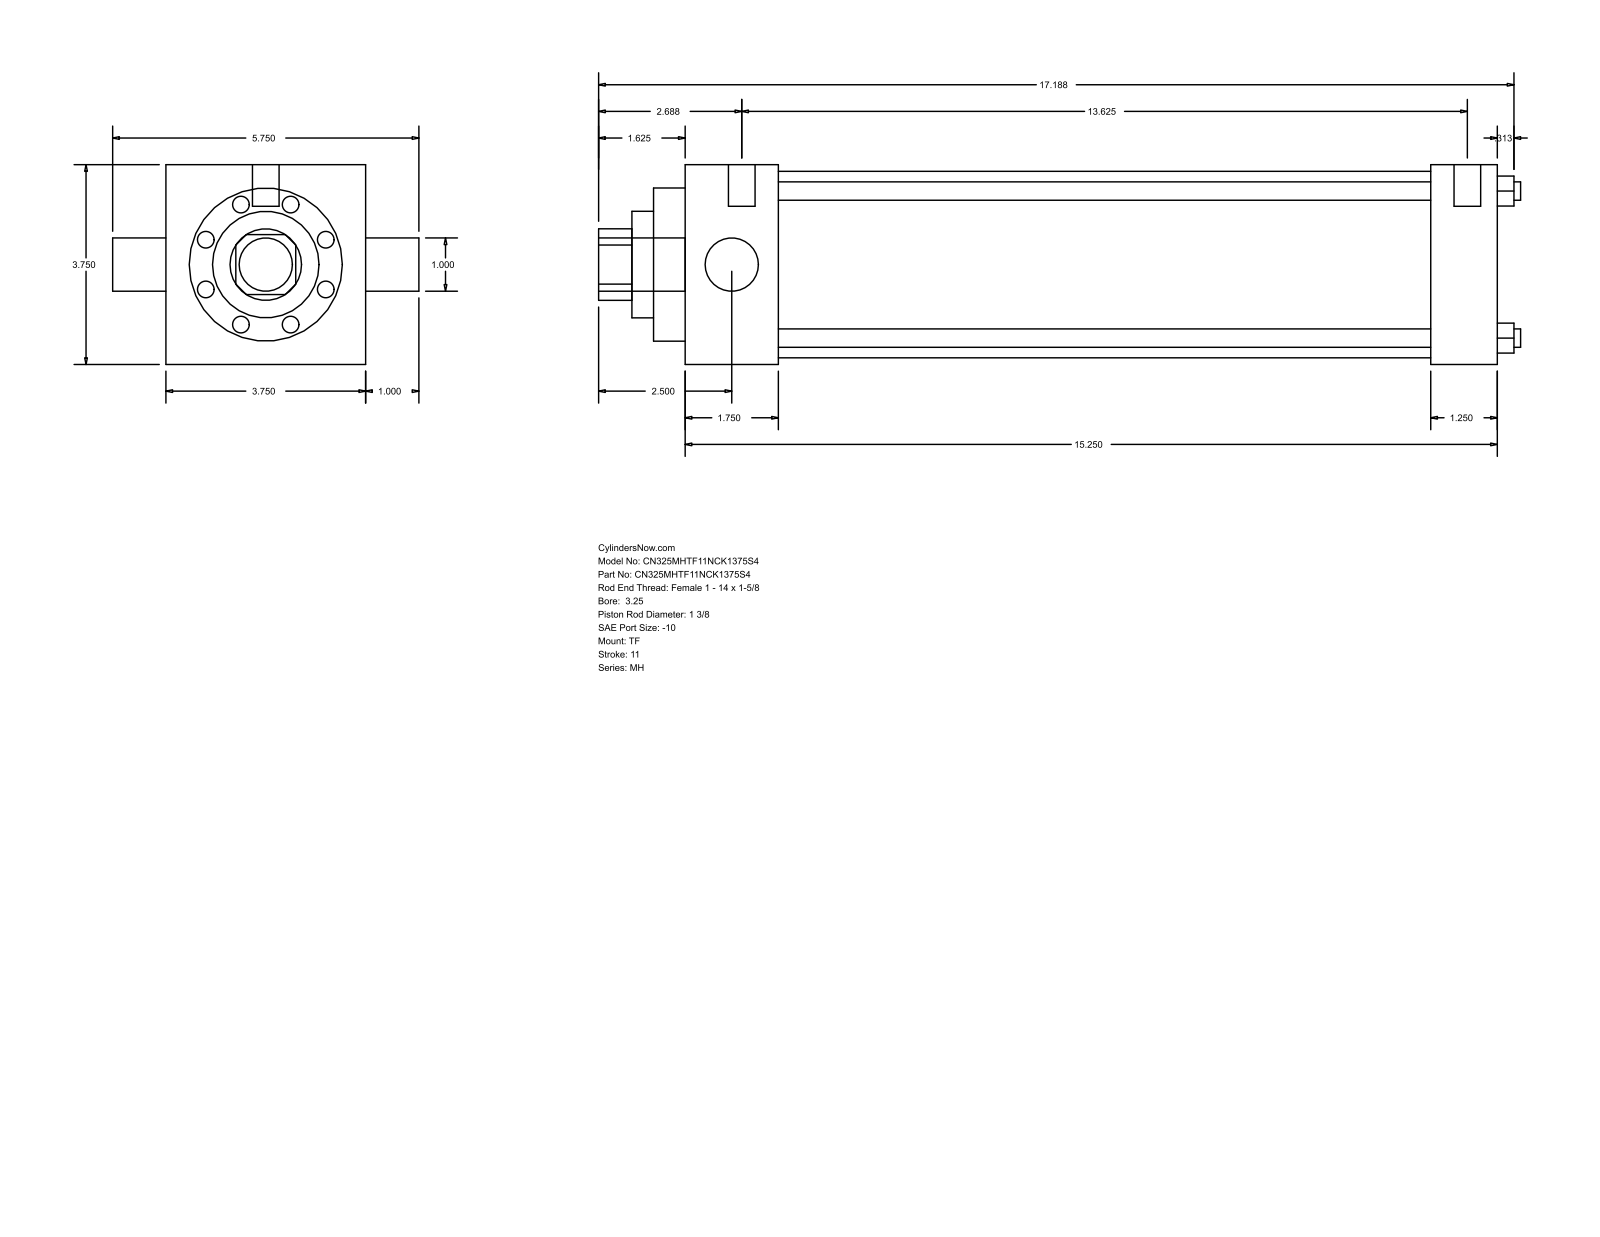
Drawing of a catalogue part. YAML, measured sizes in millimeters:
part_name: "MH_TF__0325_1.375"
step_written_by: "GSSL Pune (CONFIG_CONTROL_DESIGN)"
units: millimeters
bodies: {solids: 0, faces: 86, planar: 61, cylindrical: 25, other: 0}
overall_size: [439.74, 146.05, 95.25]
round_holes:
  - {diameter: 8.76, count: 4}
  - {diameter: 25.4, count: 1}
  - {diameter: 34.92, count: 1}
  - {diameter: 50.8, count: 1}
  - {diameter: 73.03, count: 1}
  - {diameter: 88.9, count: 1}
round_bosses_or_shafts:
  - {diameter: 5.56, count: 3}
  - {diameter: 12.7, count: 2}
  - {diameter: 25.4, count: 1}
partial_cylinders:
  - {radius: 17.06, count: 1}
face_to_face_distances: [95.24, 387.35, 44.45, 355.61, 311.16, 342.9, 31.74, 15.08, 59.53, 370.69]
hole_center_spacings: [49.57, 70.1, 99.14]
